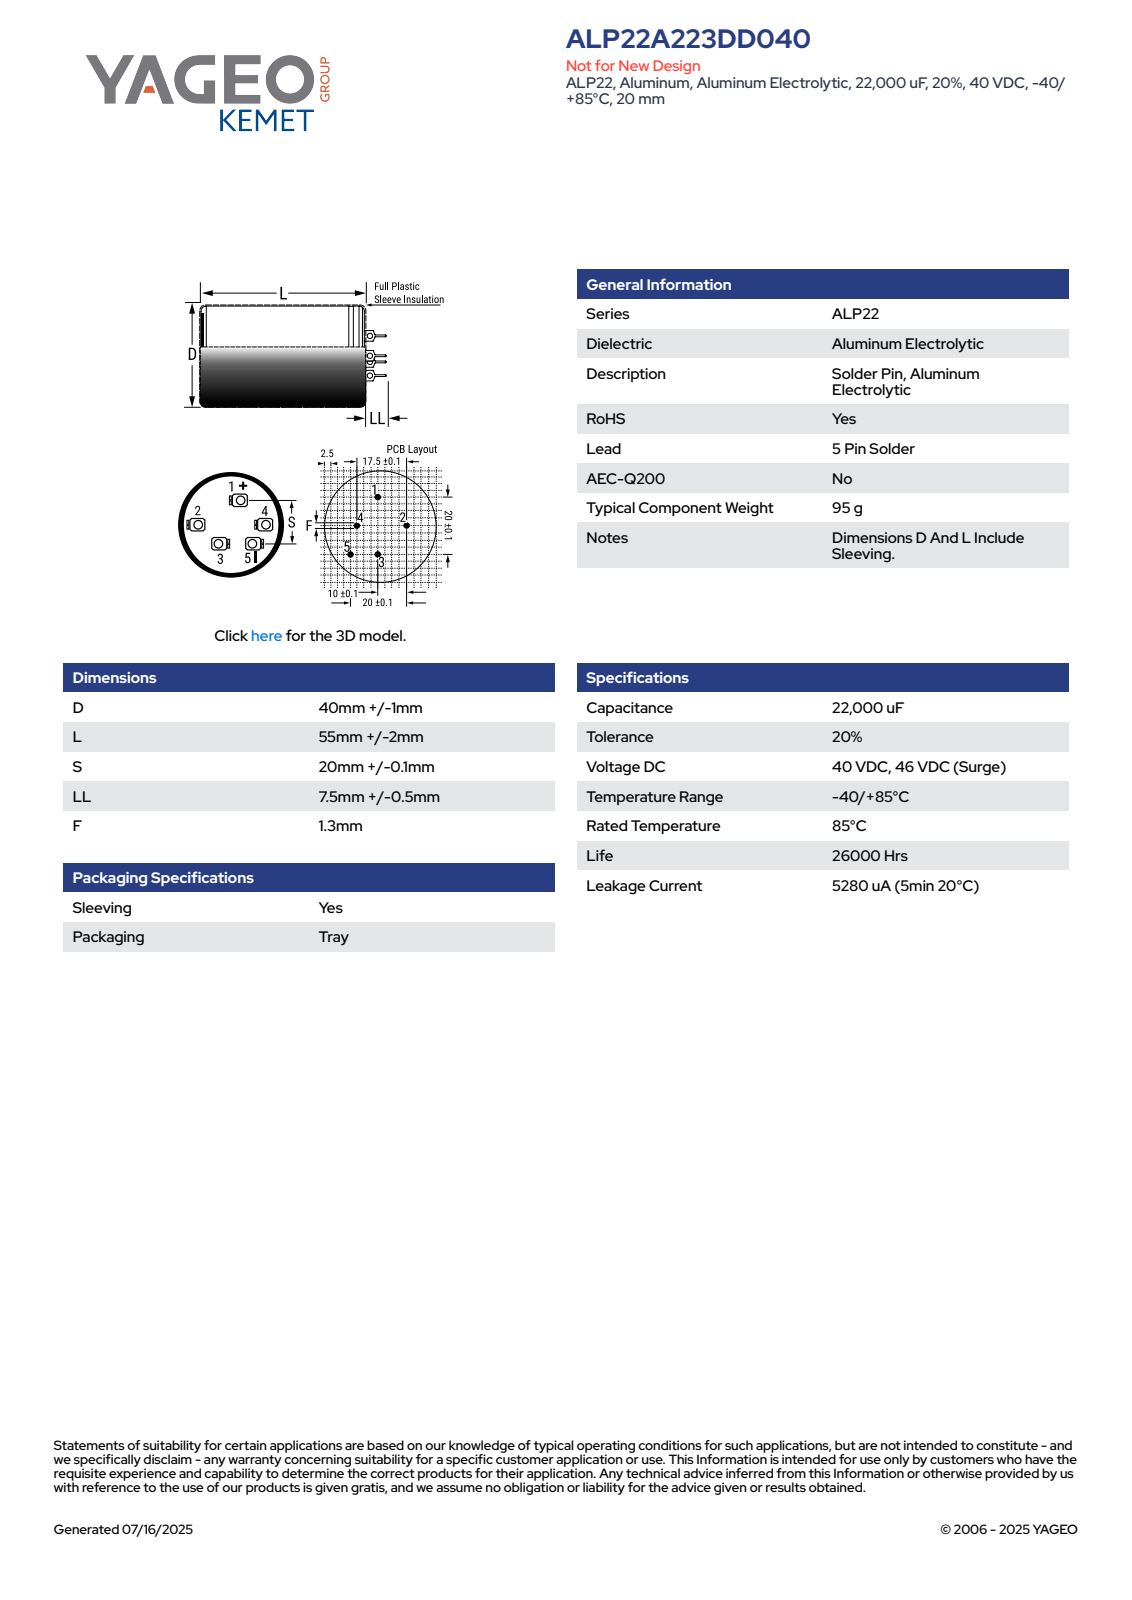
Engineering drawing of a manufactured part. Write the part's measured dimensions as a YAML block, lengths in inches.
part_name: "CARS5_D41L57LL7.5S20F1.3; Can5_1; Terminal_SolderTag7.5; Terminal_Rivet"
step_written_by: "SolidWorks 2014 (AUTOMOTIVE_DESIGN)"
units: inches
bodies: {solids: 11, faces: 269, planar: 135, cylindrical: 72, other: 62}
overall_size: [2.539, 1.614, 1.614]
volume: 4.574
surface_area: 16.03
round_holes:
  - {diameter: 0.051, count: 5}
  - {diameter: 0.039, count: 3}
round_bosses_or_shafts:
  - {diameter: 0.118, count: 5}
  - {diameter: 1.614, count: 1}
partial_cylinders:
  - {radius: 0.013, count: 3}
  - {radius: 0.807, count: 1}
face_to_face_distances: [2.244, 2.254, 0.394, 0.384, 0.295, 0.689, 0.018, 0.028, 2.272, 0.089]
hole_center_spacings: [0.394, 0.397, 0.464, 0.492, 0.557, 0.593, 0.689, 0.751]
